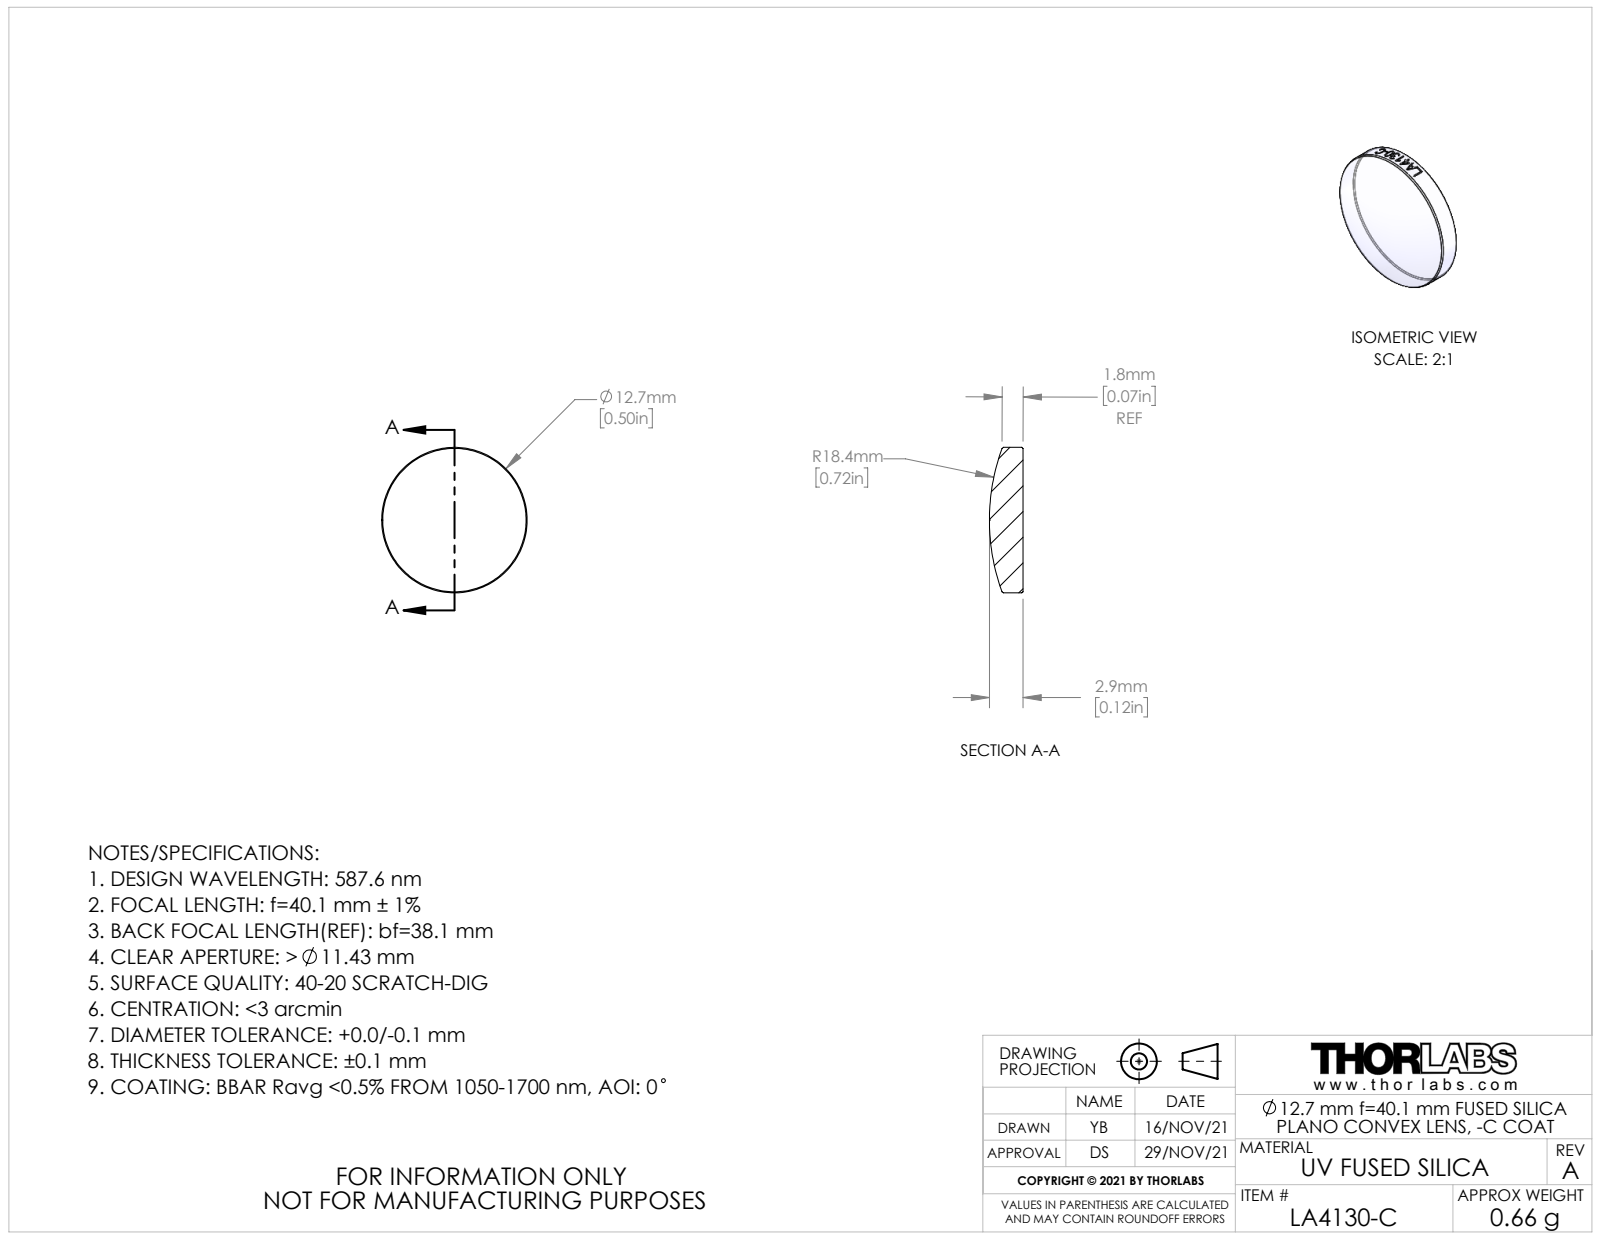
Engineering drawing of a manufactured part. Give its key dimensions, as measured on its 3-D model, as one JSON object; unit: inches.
{"part_name": "CTN018065-E0W; CTN018134", "step_written_by": "SolidWorks 2018 (AUTOMOTIVE_DESIGN)", "units": "inches", "bodies": {"solids": 1, "faces": 20, "planar": 1, "cylindrical": 13, "other": 6}, "overall_size": [0.5, 0.5, 0.115], "volume_in3": 0.018, "surface_area_in2": 0.504, "round_bosses_or_shafts": [[0.5, 1]]}
